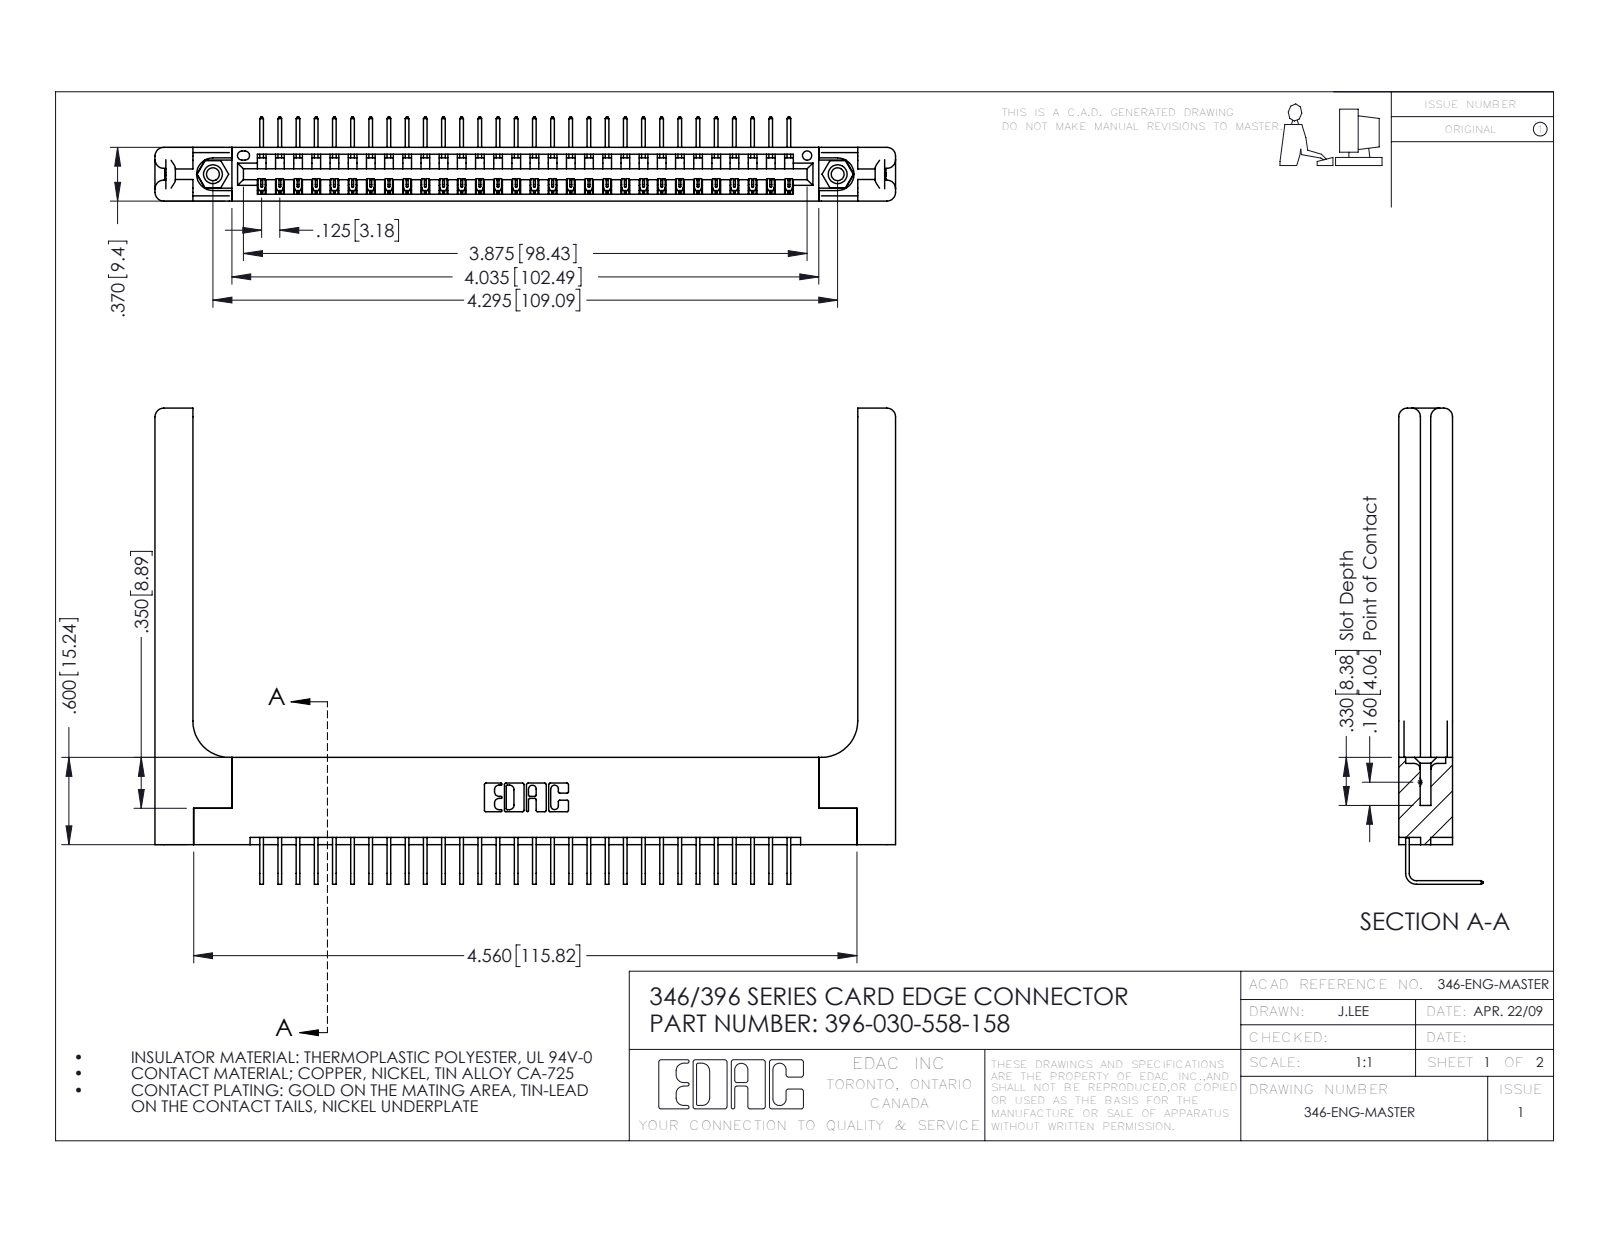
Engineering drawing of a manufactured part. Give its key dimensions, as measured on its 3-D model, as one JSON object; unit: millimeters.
{"part_name": "346-220-058_345-220-058; 345-292-001_558 Tail - 2; 345-250-001_345-250-001-102; 346 Part_Flush Mounting Lugs - 0.156 Dia-TH (+1 more)", "step_written_by": "SolidWorks 2016 (CONFIG_CONTROL_DESIGN)", "units": "millimeters", "bodies": {"solids": 35, "faces": 2178, "planar": 1484, "cylindrical": 634, "other": 60}, "overall_size": [129.3, 83.1, 14.7], "volume_mm3": 19910, "surface_area_mm2": 21130, "round_holes": [[2.3, 2], [3.2, 2], [4, 2], [1.6, 1]], "round_bosses_or_shafts": [[3.9, 2]], "partial_cylinders_radius": [[0.2, 60], [0.3, 22], [1.5, 16], [0.2, 6], [0.8, 6], [0.7, 3], [0.8, 2], [0.8, 2]], "face_to_face_distances": [9.4, 8.2, 1.8, 1.2, 3.8, 3.8, 6.4, 0.6, 7.6, 1.9], "hole_center_spacings": [6.2, 103.8, 109.1]}
